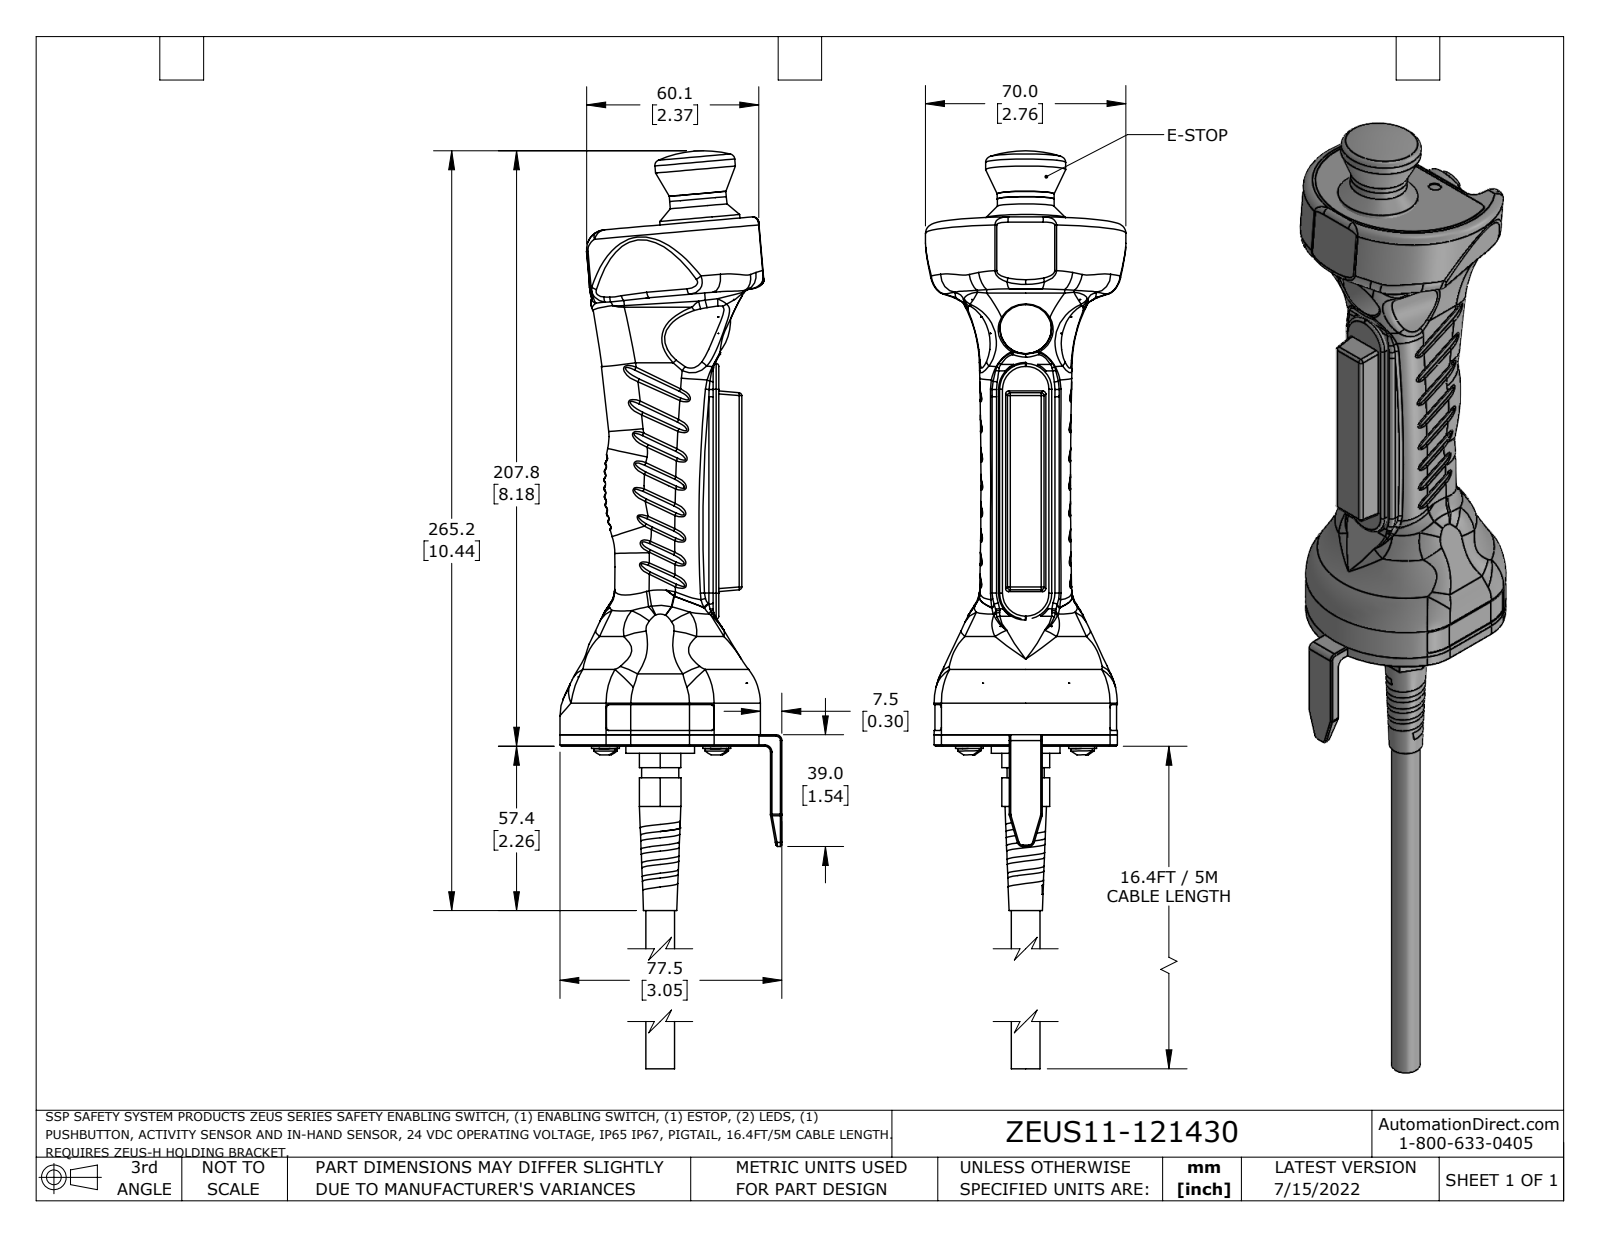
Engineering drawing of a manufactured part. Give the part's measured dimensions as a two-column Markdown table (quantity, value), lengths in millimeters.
| quantity | value |
| --- | --- |
| part name | ZEUS11-121430 |
| STEP written by | SolidWorks 2021 (AUTOMOTIVE_DESIGN) |
| units | millimeters |
| bodies | 21 solids, 1439 faces (502 planar, 469 cylindrical, 468 other) |
| overall size | 402.2 × 77.5 × 70 |
| volume | 407 100 mm³ |
| surface area | 89 740 mm² |
| round holes (diameter × count) | 3.4 × 4, 4.3 × 4, 4.5 × 4, 5 × 4, 2.5 × 2, 2.8 × 2, 4.2 × 2, 4.4 × 2, 8.4 × 2, 1 × 1, 4 × 1, 5.1 × 1 |
| round bosses / shafts (diameter × count) | 9 × 4, 7.5 × 4, 4 × 4, 1 × 4, 28 × 2, 19.8 × 2, 11.7 × 2, 6 × 2 |
| partial cylindrical surfaces (radius × count) | 0.1 × 96, 1 × 51, 0.7 × 48, 2 × 27, 0.2 × 22, 3 × 10, 0.2 × 8, 0.8 × 7 |
| main face-to-face distances | 4, 2, 0.4, 0.5, 1.7, 1.5, 2.5, 1, 4.5, 4.1 |
| hole center spacings | 10.3, 16, 22, 27.4, 30, 38.9, 39.6, 13 |
